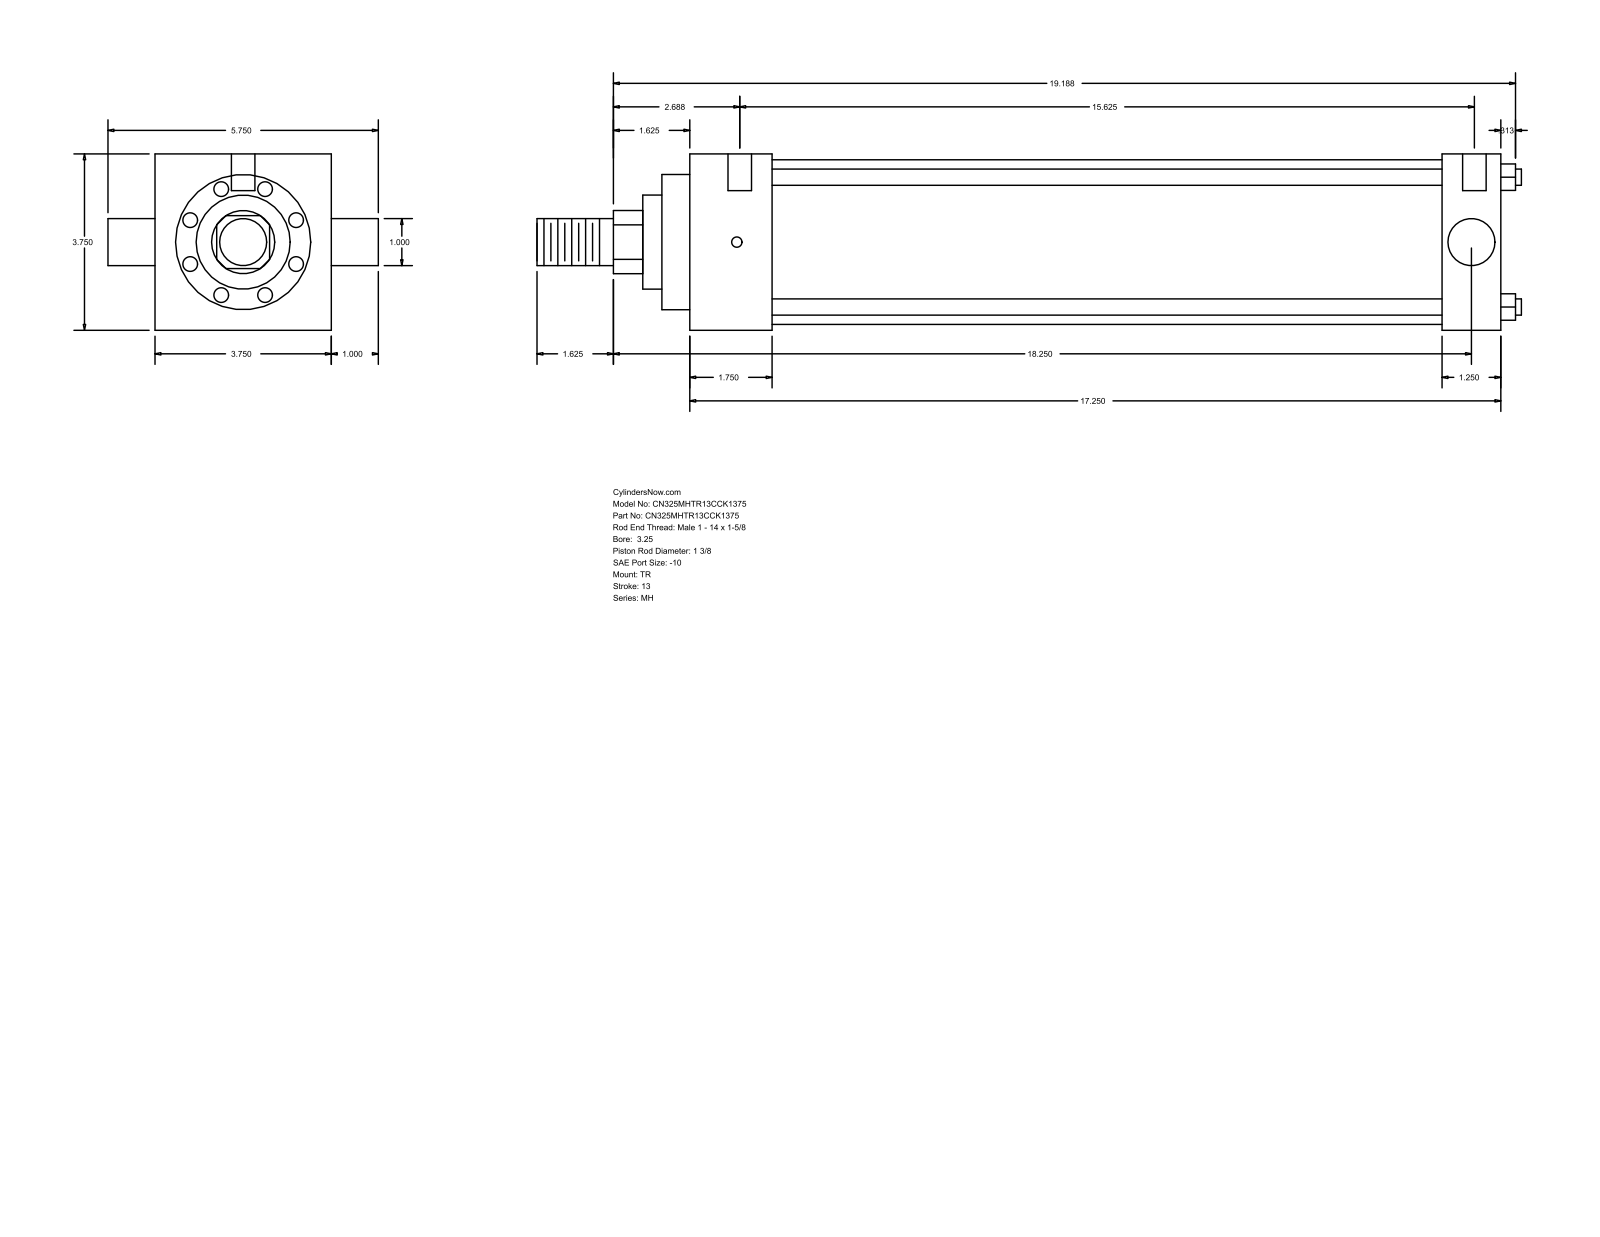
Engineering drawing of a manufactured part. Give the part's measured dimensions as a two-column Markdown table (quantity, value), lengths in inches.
| quantity | value |
| --- | --- |
| part name | MH_TR__0325_1.375 |
| STEP written by | GSSL Pune (CONFIG_CONTROL_DESIGN) |
| units | inches |
| bodies | 0 solids, 86 faces (61 planar, 25 cylindrical, 0 other) |
| overall size | 20.937 × 5.75 × 3.75 |
| round holes (diameter × count) | 0.219 × 3, 0.5 × 2 |
| round bosses / shafts (diameter × count) | 0.345 × 4, 1 × 2, 3.5 × 1, 2.875 × 1, 2 × 1, 1.375 × 1 |
| partial cylindrical surfaces (radius × count) | 0.672 × 1 |
| main face-to-face distances | 3.75, 17.25, 1.75, 16, 14.25, 15.5, 1.25, 0.594, 2.344, 16.594 |
| hole center spacings | 0.063, 0.187, 15.625, 15.688, 15.813, 15.875 |
